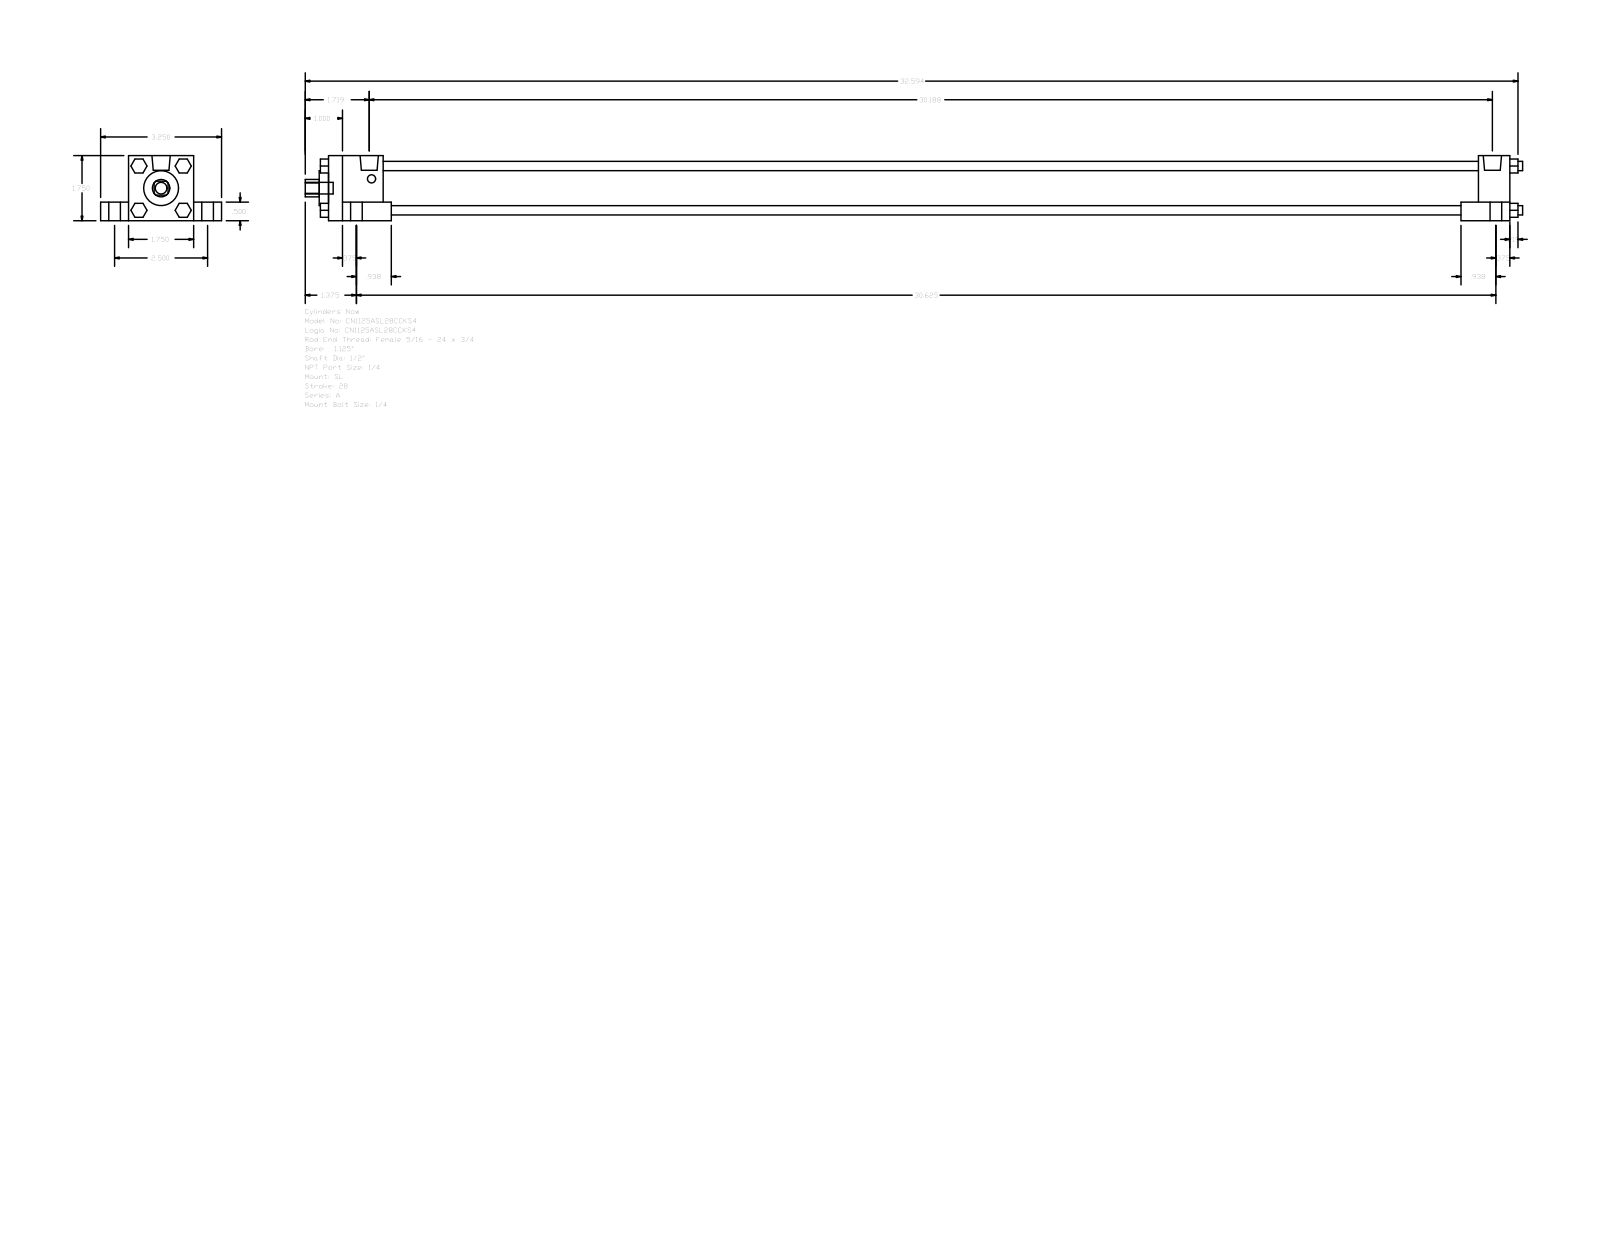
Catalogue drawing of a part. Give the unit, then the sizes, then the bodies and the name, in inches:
Units: inches
Overall size (bounding box): 32.719 × 3.25 × 1.75
Round holes (diameter × count): ⌀0.5 ×1, ⌀0.937 ×1, ⌀1.255 ×1
Round bosses / shafts (diameter × count): ⌀0.313 ×5, ⌀0.563 ×4, ⌀0.25 ×4, ⌀0.219 ×4, ⌀0.492 ×2
Partial cylindrical surfaces — rounded edges, fillets, slot ends (radius × count): R0.234 ×1
Main face-to-face distances: 1.75, 1.25, 0.5, 0.75, 2.5, 31.75, 30.906, 0.844, 1.469, 29.437
Bodies: 0 solids, 150 faces (114 planar, 36 cylindrical, 0 other)
Part name (STEP PRODUCT): A_SL__0112_0.5
STEP written by: GSSL Pune (CONFIG_CONTROL_DESIGN)
